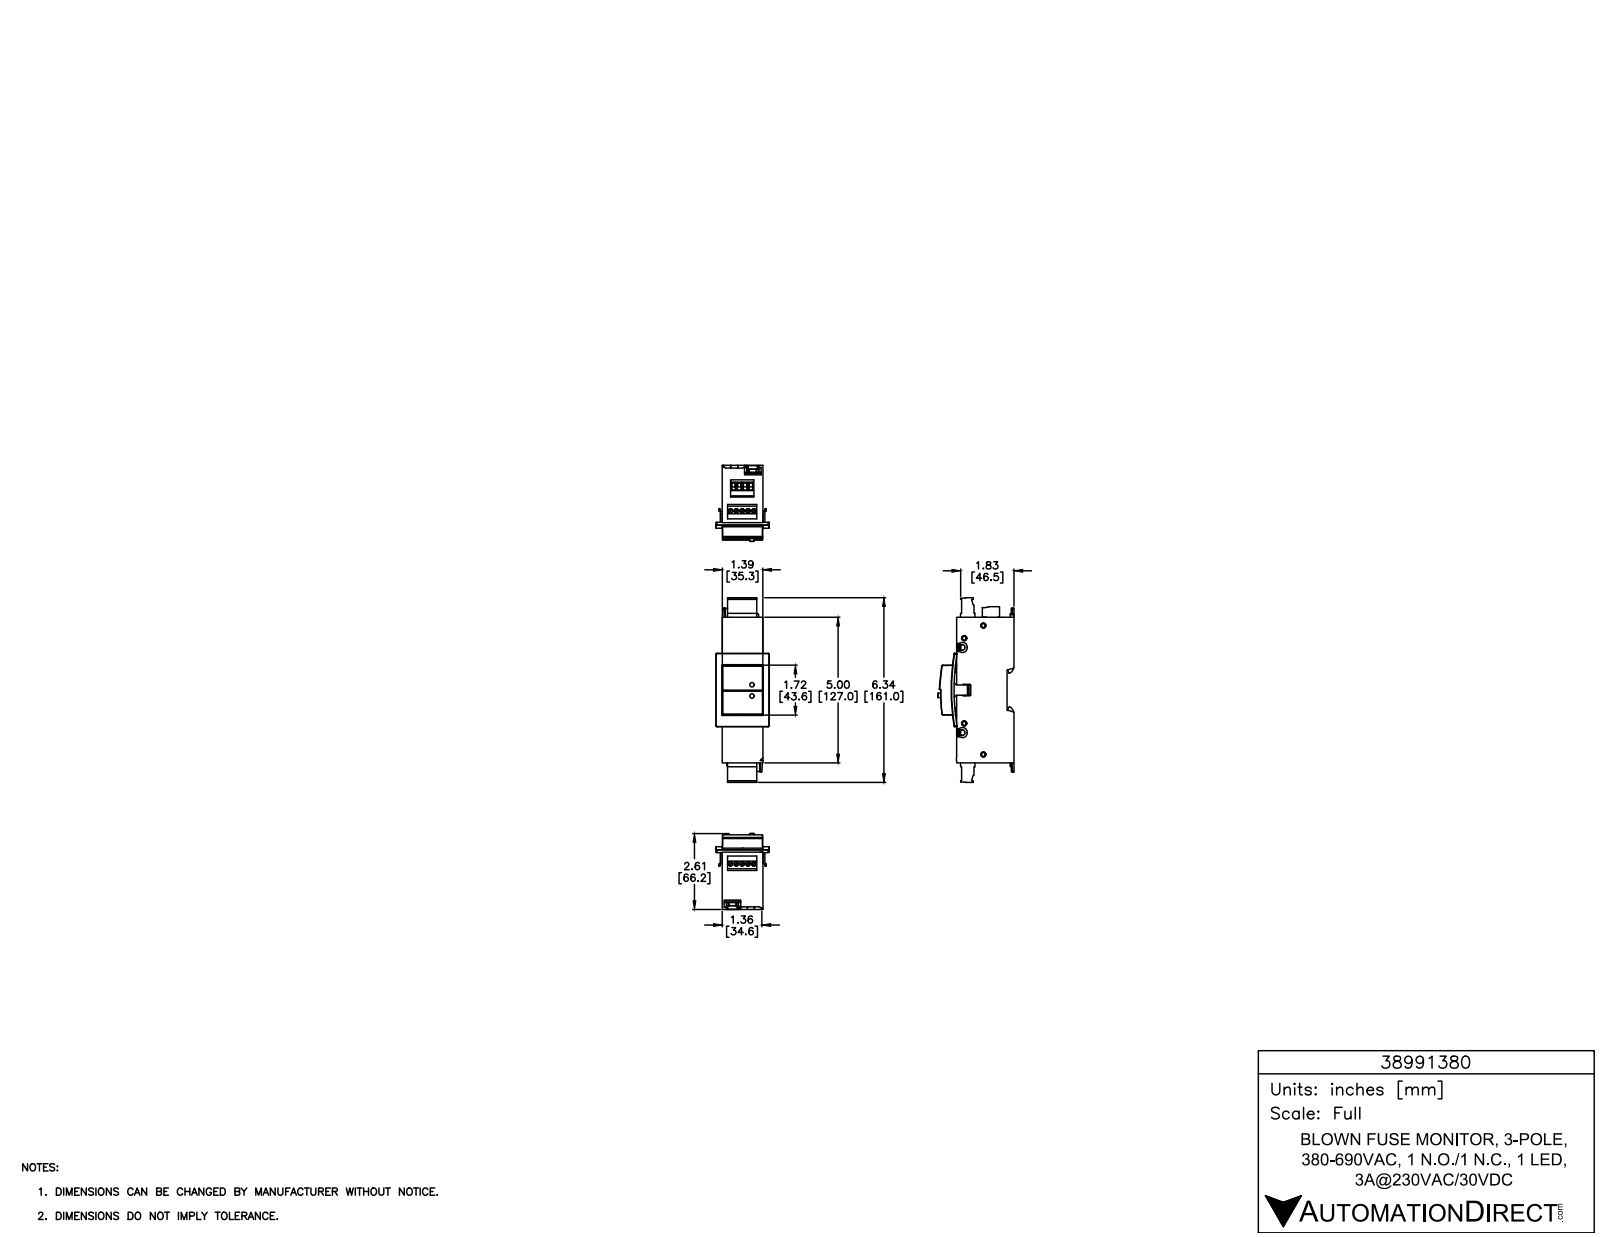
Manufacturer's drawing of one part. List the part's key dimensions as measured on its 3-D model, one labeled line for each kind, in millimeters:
Part name (STEP PRODUCT): 38991380
STEP written by: SolidWorks 2015 (AUTOMOTIVE_DESIGN)
Units: millimetres
Bodies: 1 solid, 847 faces (521 planar, 248 cylindrical, 78 other)
Overall size (bounding box): 161 × 66.4 × 46.5
Volume: 243 300 mm³ · Surface area: 44 520 mm²
Round holes (diameter × count): ⌀4 ×9, ⌀4.6 ×4, ⌀4.2 ×2
Round bosses / shafts (diameter × count): ⌀3.8 ×9, ⌀4.2 ×4
Partial cylindrical surfaces — rounded edges, fillets, slot ends (radius × count): R0.2 ×24, R0.2 ×24, R0.6 ×24, R1 ×15, R0.3 ×12, R0.5 ×10, R1.2 ×4, R1.5 ×4
Main face-to-face distances: 35.5, 44, 50, 6, 127, 17.8, 10.2, 5.4, 4.3, 39.7
Hole centre spacings: 5.1, 10.2, 15.2, 9.8, 20.1, 20.3, 31.9, 62.7
